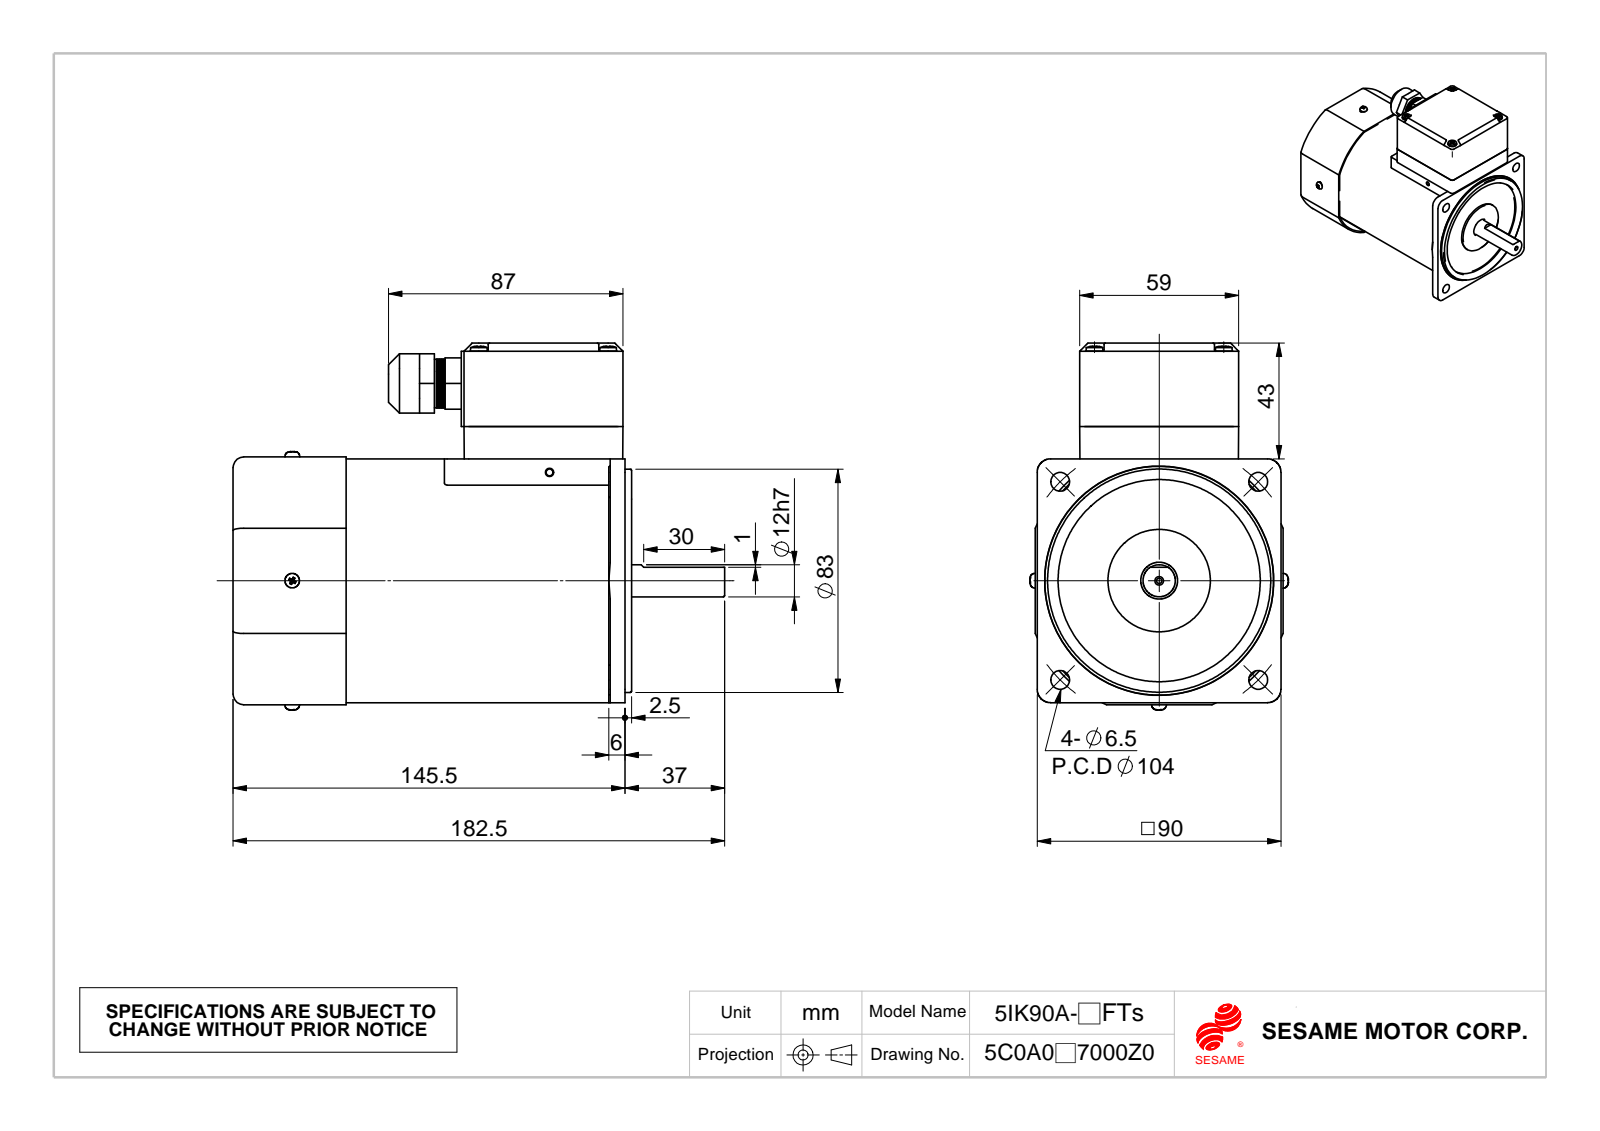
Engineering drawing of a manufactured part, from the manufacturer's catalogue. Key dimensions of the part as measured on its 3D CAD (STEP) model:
Part name (STEP PRODUCT): 90A_4.研磨; 風扇蓋FC-9042-21; M590Ts-F; 成品180度 (+1 more)
STEP written by: SolidWorks 2010 (CONFIG_CONTROL_DESIGN)
Units: millimetres
Bodies: 16 solids, 2685 faces (330 planar, 936 cylindrical, 1419 other)
Overall size (bounding box): 182.5 × 136.21 × 95.92
Volume: 1 034 000 mm³ · Surface area: 148 333 mm²
Round holes (diameter × count): ⌀3.3 ×4, ⌀3.5 ×4, ⌀3.9 ×4, ⌀4.3 ×4, ⌀7 ×4, ⌀2.5 ×3, ⌀2 ×1, ⌀6.5 ×1, ⌀11 ×1, ⌀12 ×1, ⌀13.7 ×1, ⌀14.5 ×1
Round bosses / shafts (diameter × count): ⌀3 ×6, ⌀6.3 ×4, ⌀11 ×3, ⌀5.5 ×2, ⌀90.5 ×1, ⌀86 ×1, ⌀85 ×1, ⌀84 ×1
Partial cylindrical surfaces — rounded edges, fillets, slot ends (radius × count): R0.3 ×16, R2 ×16, R1 ×10, R4 ×10, R0.5 ×8, R3 ×8, R1.5 ×4, R1.75 ×4
Main face-to-face distances: 1, 12, 0.75, 91, 3.9, 16, 139, 142.9, 140, 143.9
Hole centre spacings: 48, 52, 73.54, 11.67, 12.35, 12.7, 24.93, 25
